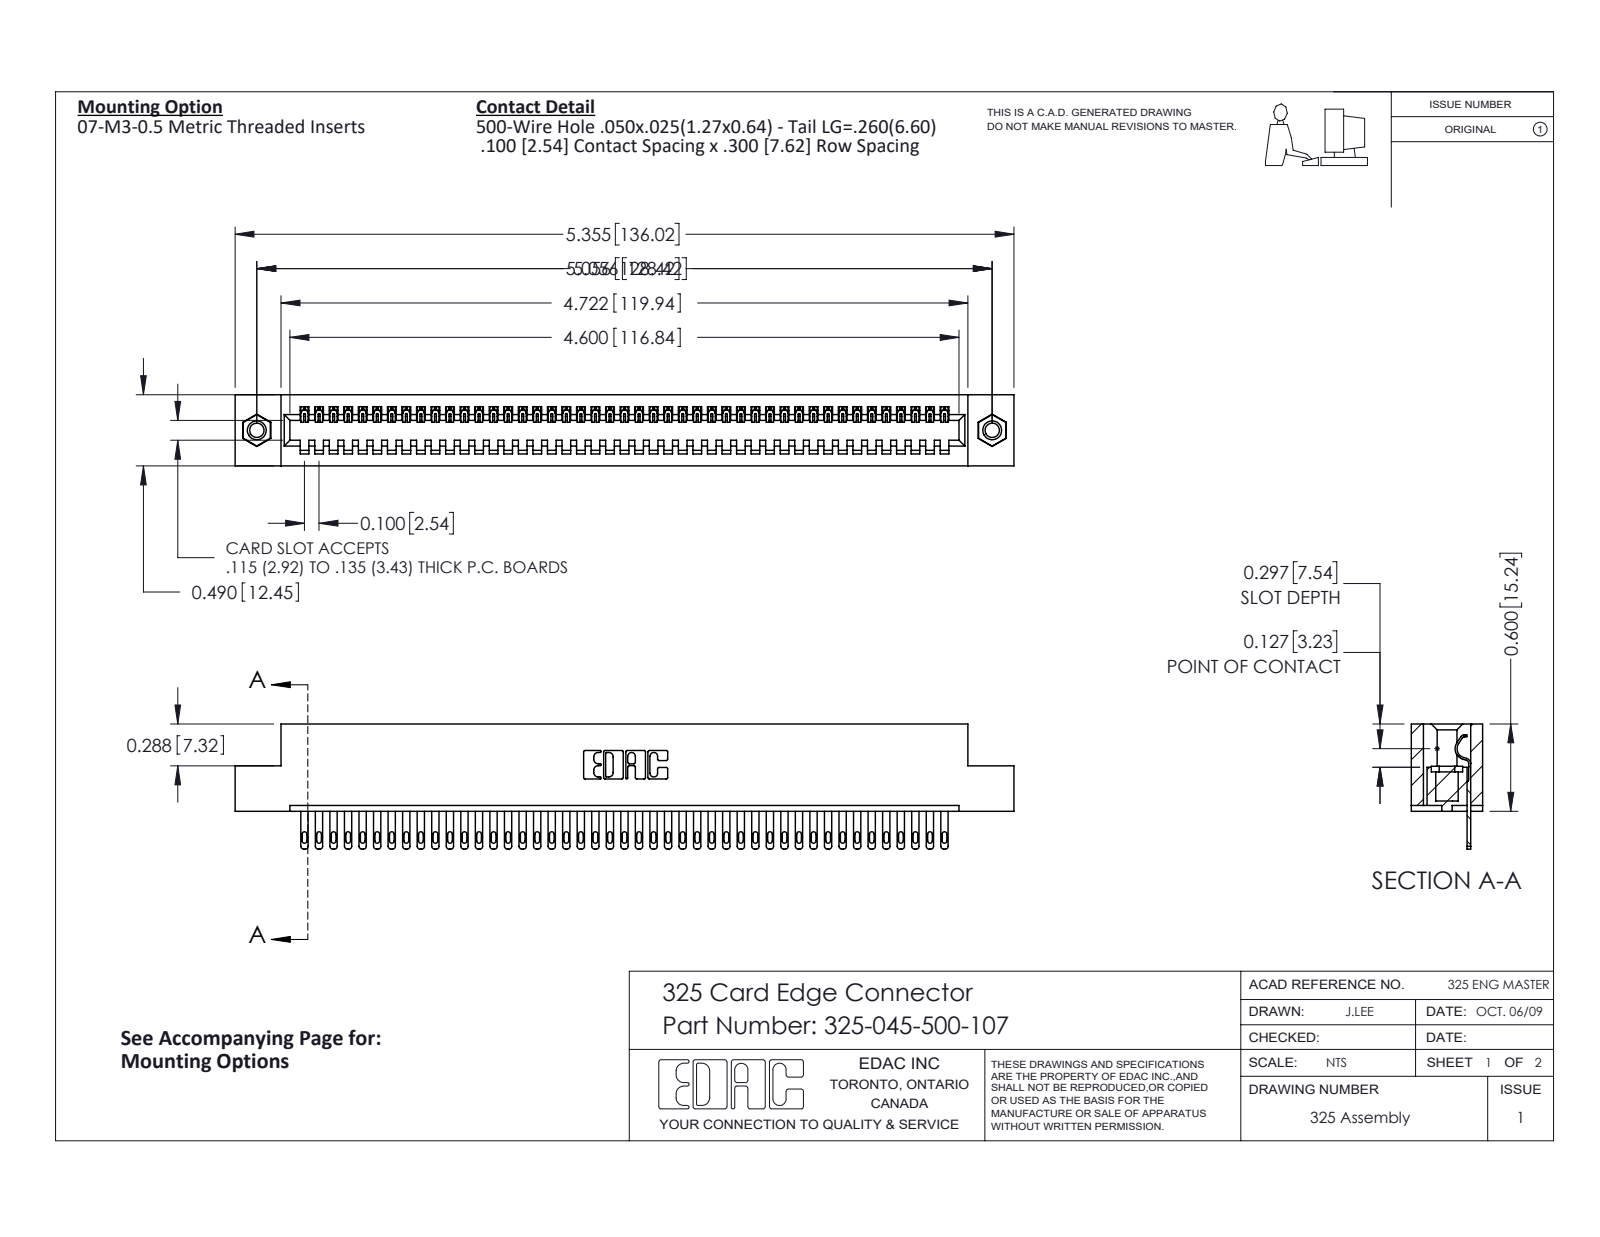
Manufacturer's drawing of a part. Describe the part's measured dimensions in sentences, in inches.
The part is named "325-292-001_325-293-100; 325 Part_TI; 345-250-001_345-250-005-103; 325-045-500-107". Its 3-D file was written by "SolidWorks 2016 (CONFIG_CONTROL_DESIGN)". It is 48 solids with 2604 faces: 1722 planar, 866 cylindrical and 16 other. Overall it measures 5.355 by 0.86 by 0.49 inches. Its volume is 1.056 cubic inches and its surface area 29.59 square inches. Round holes: 2 of diameter 0.098, 2 of diameter 0.125, 2 of diameter 0.16. Round bosses or shafts: 2 of diameter 0.155. Partial cylindrical surfaces (rounded edges, fillets, slot ends): 90 of radius 0.006, 90 of radius 0.016, 90 of radius 0.02, 22 of radius 0.01, 6 of radius 0.007, 6 of radius 0.031, 3 of radius 0.026, 1 of radius 0.014. The main face-to-face distances are 0.083, 0.407, 0.49, 0.3, 0.107, 0.383, 0.025, 0.325, 0.56, 0.263. The hole center spacings are 5.056.
